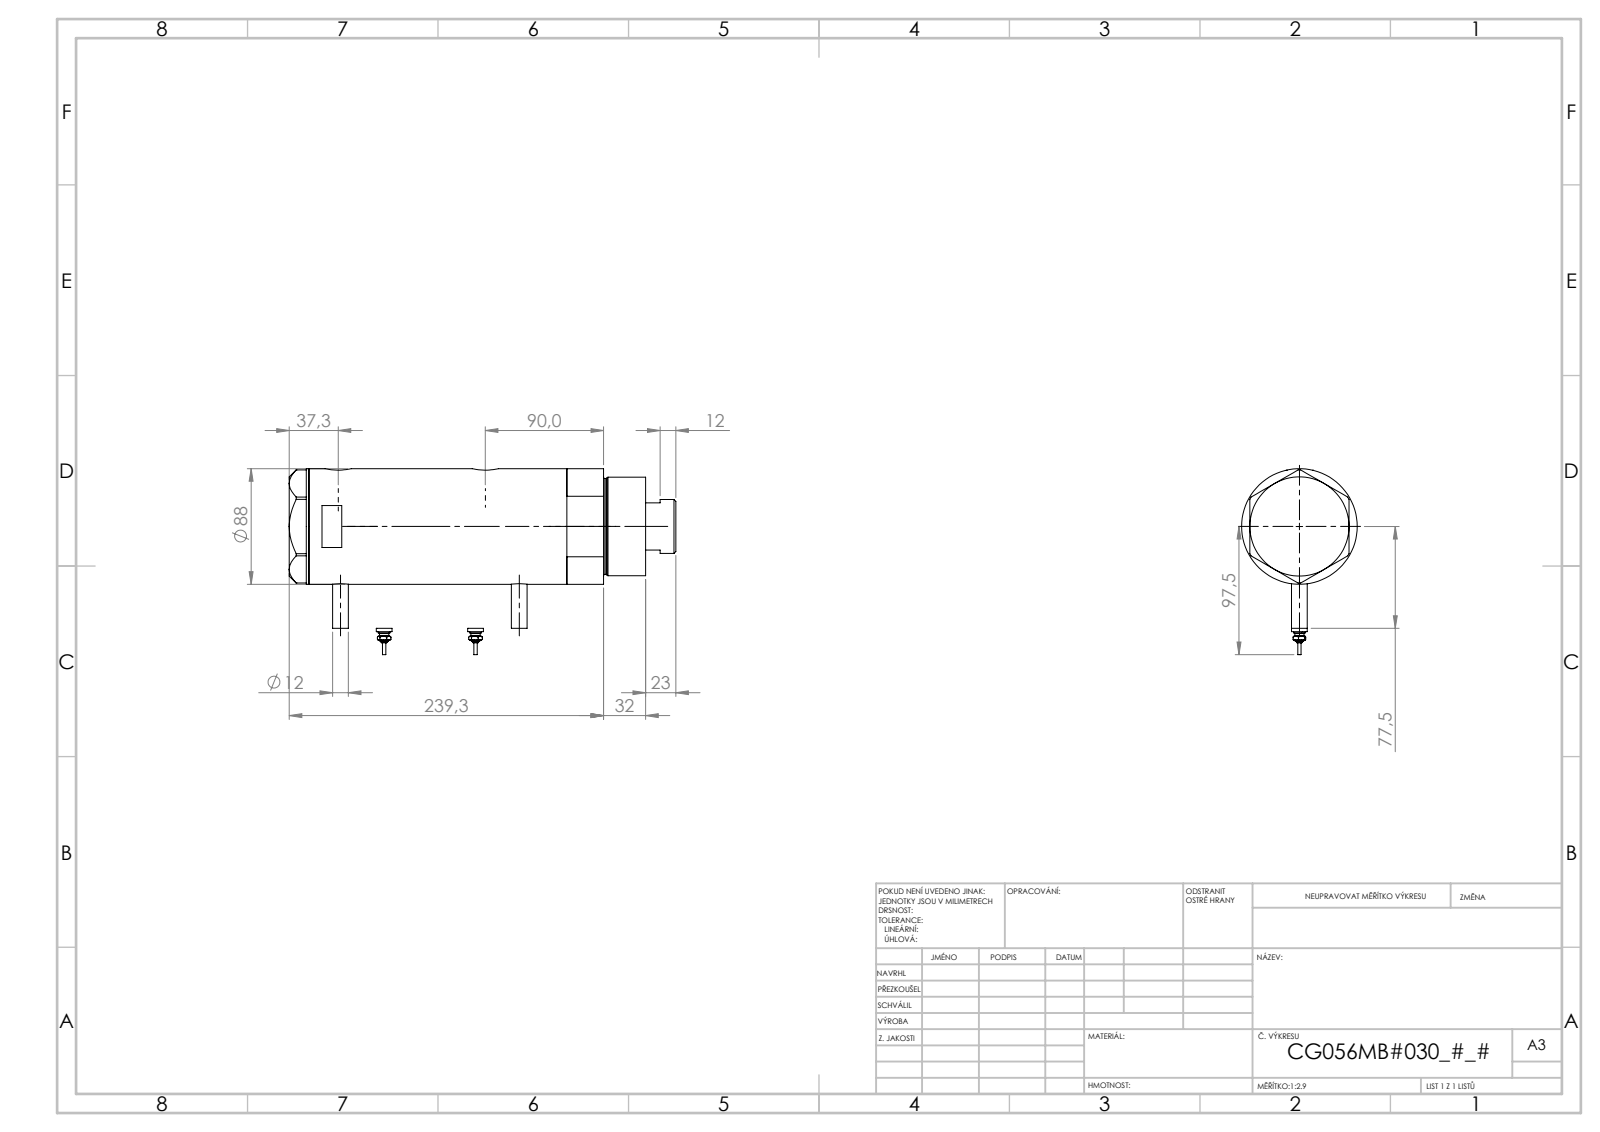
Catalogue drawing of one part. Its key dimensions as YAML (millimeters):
part_name: "Switch; V270CG_BACK; V270CG_FRONT; V270CG_MIDDLE (+1 more)"
step_written_by: "SolidWorks 2019 (CONFIG_CONTROL_DESIGN)"
units: millimeters
bodies: {solids: 6, faces: 213, planar: 80, cylindrical: 69, other: 64}
overall_size: [294.3, 141.5, 88]
volume: 1563000
surface_area: 225469
round_holes:
  - {diameter: 12.5, count: 2}
  - {diameter: 13.16, count: 2}
  - {diameter: 20, count: 2}
  - {diameter: 14.5, count: 1}
  - {diameter: 42, count: 1}
  - {diameter: 43.5, count: 1}
  - {diameter: 56, count: 1}
  - {diameter: 60, count: 1}
  - {diameter: 80, count: 1}
round_bosses_or_shafts:
  - {diameter: 12, count: 4}
  - {diameter: 9, count: 2}
  - {diameter: 7, count: 2}
  - {diameter: 4.5, count: 2}
  - {diameter: 2.5, count: 2}
  - {diameter: 88, count: 1}
  - {diameter: 75, count: 1}
  - {diameter: 73, count: 1}
face_to_face_distances: [134.4, 26, 108.4, 15, 41, 149.4, 256.3, 271.3, 230.3, 121.9]
hole_center_spacings: [1.7, 25.8, 110.3, 112, 136.1, 137.8]
